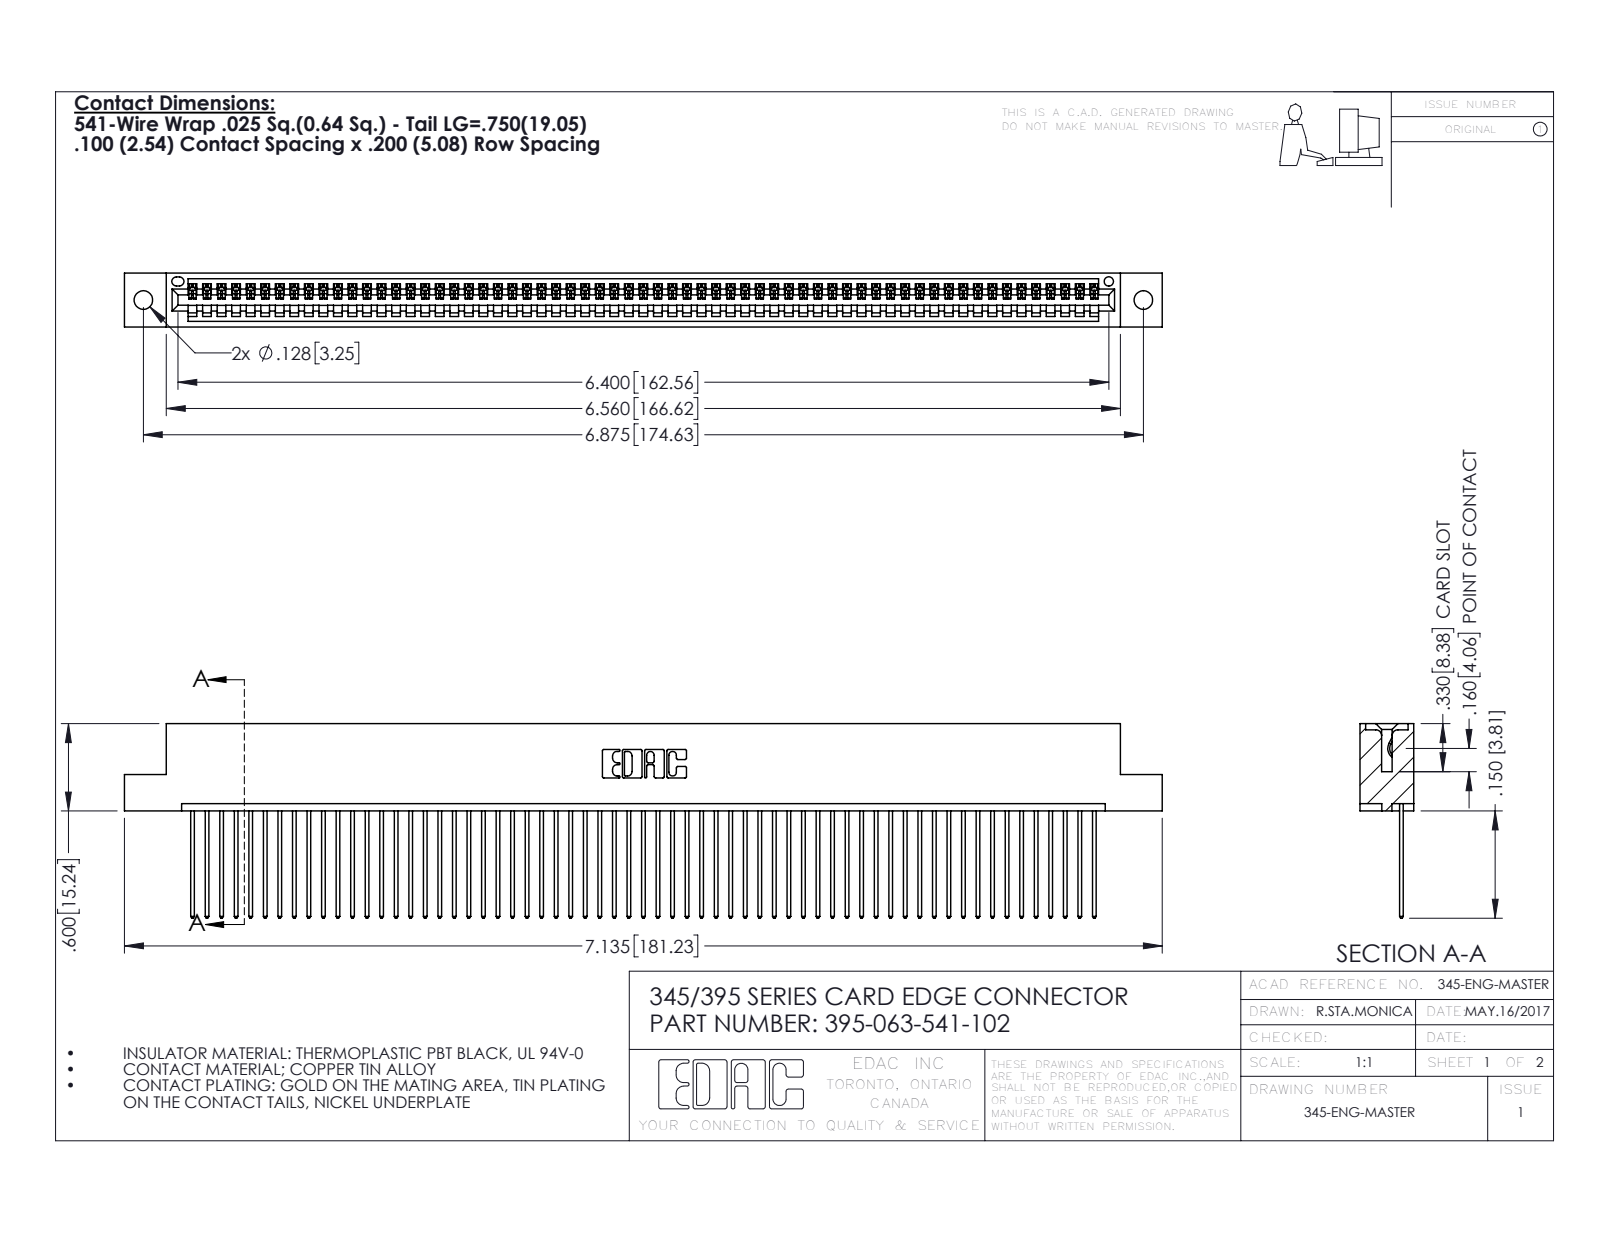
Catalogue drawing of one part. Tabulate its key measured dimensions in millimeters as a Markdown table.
| quantity | value |
| --- | --- |
| part name | 345-292-001_345-293-141; 345 Part_Flush Mounting Lugs - 0.128 Dia; 395-063-541-102 |
| STEP written by | SolidWorks 2016 (CONFIG_CONTROL_DESIGN) |
| units | millimeters |
| bodies | 64 solids, 3780 faces (2600 planar, 1180 cylindrical, 0 other) |
| overall size | 181.2 × 34 × 9.4 |
| volume | 17 550 mm³ |
| surface area | 24 570 mm² |
| round holes (diameter × count) | 3.3 × 2, 1.6 × 1 |
| partial cylindrical surfaces (radius × count) | 0.2 × 126, 0.3 × 126, 0.3 × 22, 0.2 × 6, 0.8 × 6, 0.7 × 3, 0.8 × 2, 1 × 2 |
| main face-to-face distances | 1.8, 7.6, 2.5, 6.9, 0.6, 9.4, 5.1, 5.7, 3.8, 1.8 |
| hole center spacings | 6.9, 168.6, 174.6 |
